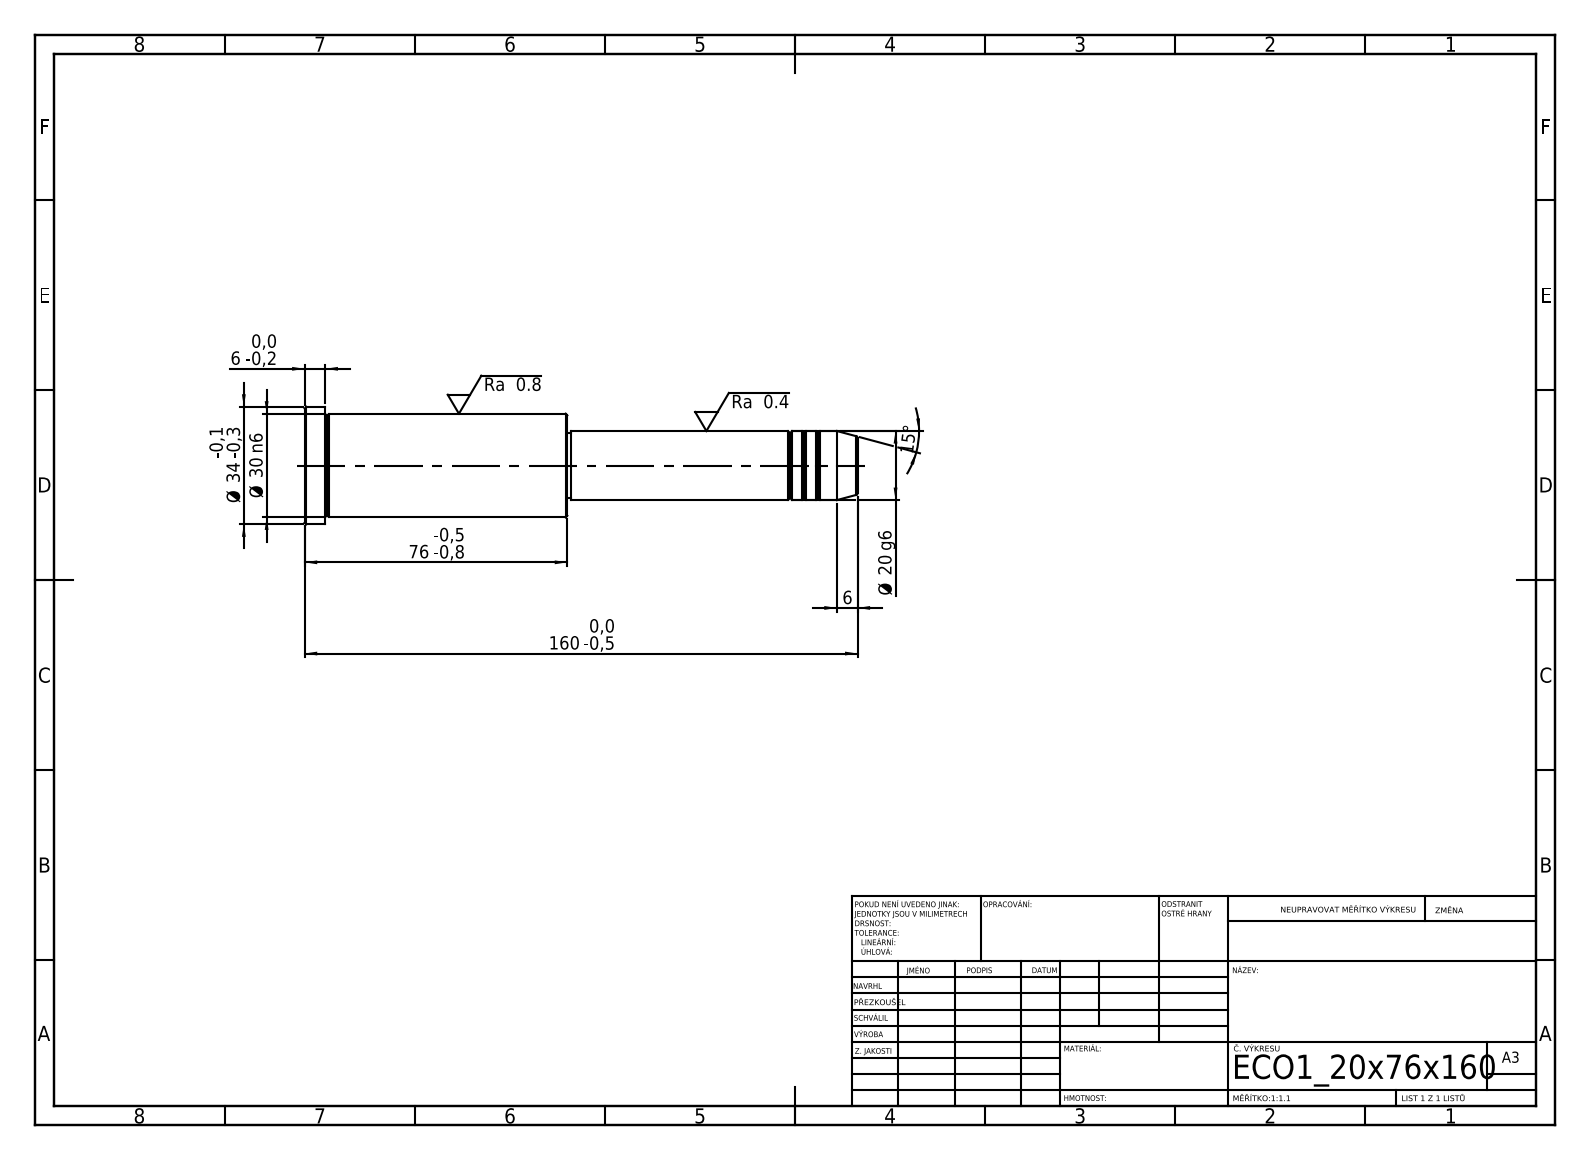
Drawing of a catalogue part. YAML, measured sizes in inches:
step_written_by: "SolidWorks 2019 (CONFIG_CONTROL_DESIGN)"
units: inches
bodies: {solids: 1, faces: 43, planar: 5, cylindrical: 14, other: 24}
overall_size: [6.299, 1.339, 1.339]
volume: 4.935
surface_area: 22.26
round_bosses_or_shafts:
  - {diameter: 1.339, count: 1}
  - {diameter: 1.181, count: 1}
  - {diameter: 0.787, count: 1}
  - {diameter: 0.748, count: 1}
face_to_face_distances: [2.992, 3.307, 6.299, 6.063, 2.756, 0.236, 3.268, 0.039, 2.795, 3.031]
